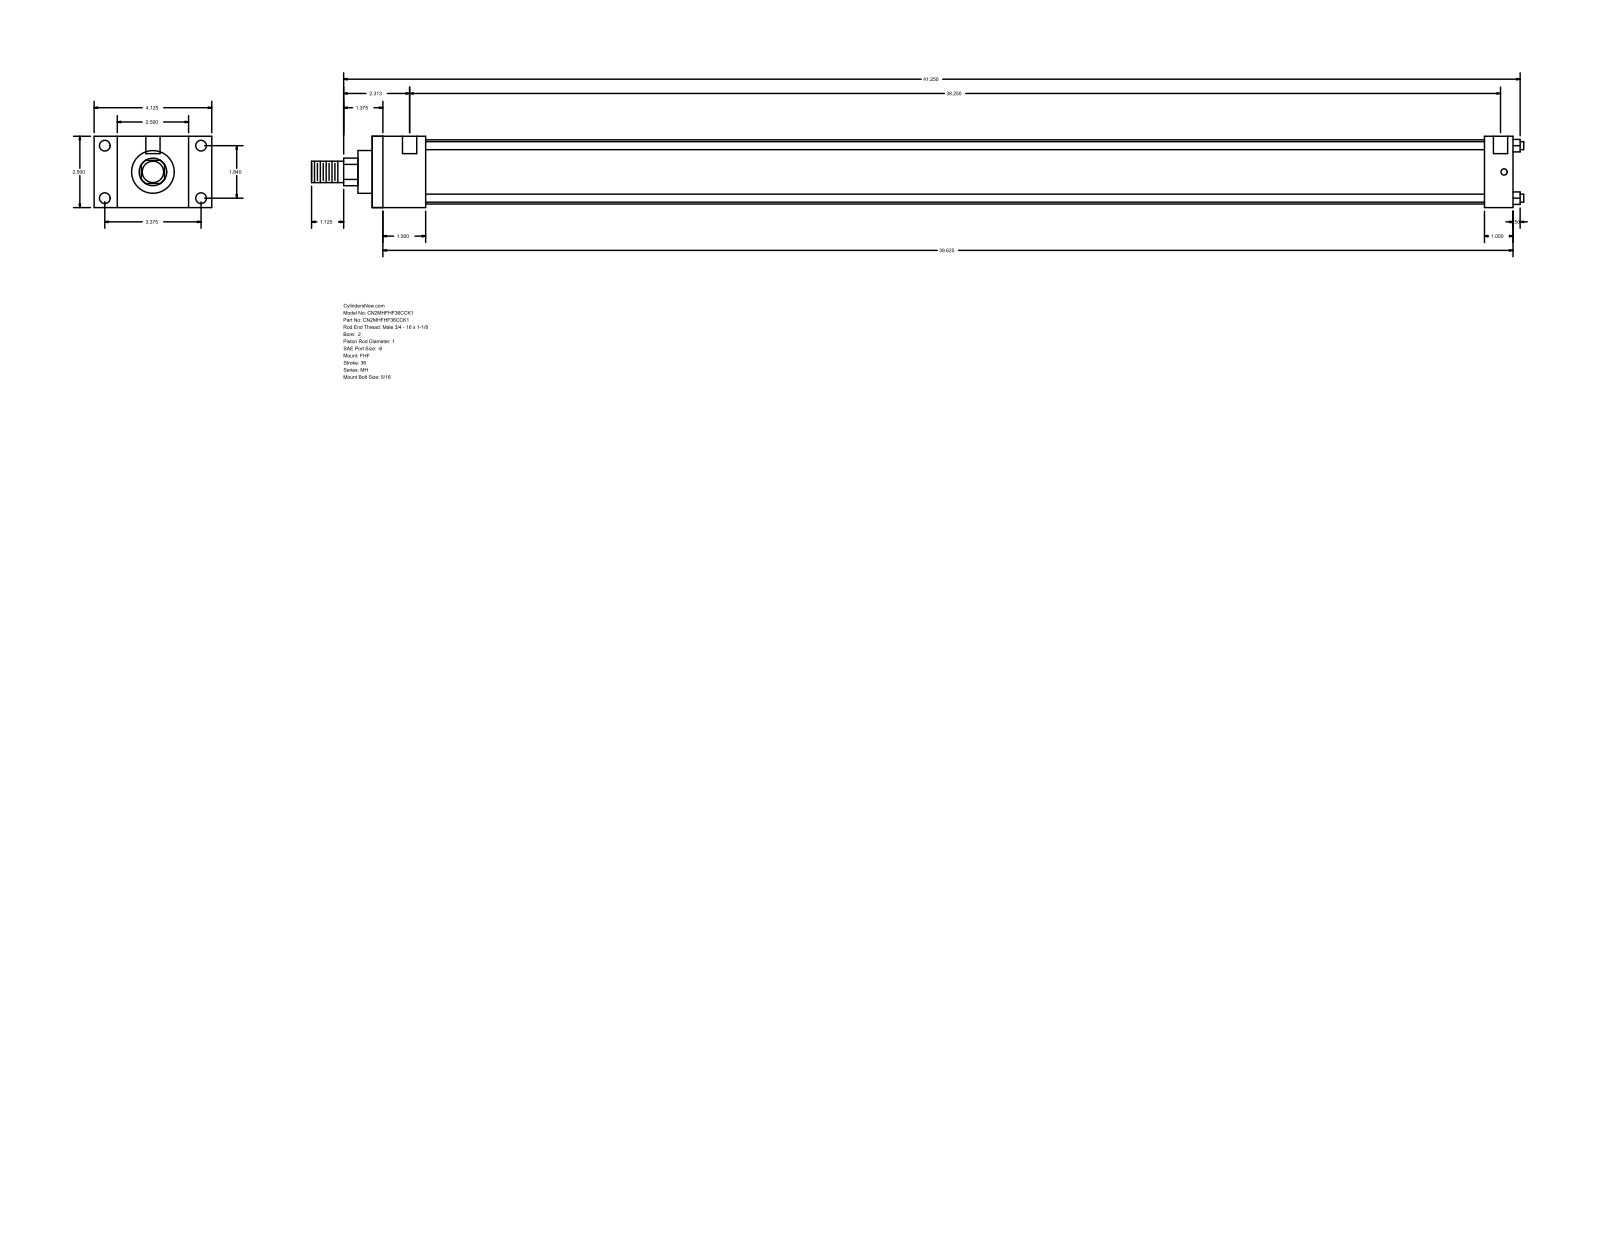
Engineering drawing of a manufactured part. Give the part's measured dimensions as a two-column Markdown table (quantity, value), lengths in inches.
| quantity | value |
| --- | --- |
| part name | MH_FHF__0200_1 |
| STEP written by | GSSL Pune (CONFIG_CONTROL_DESIGN) |
| units | inches |
| bodies | 0 solids, 88 faces (60 planar, 28 cylindrical, 0 other) |
| overall size | 42.5 × 4.125 × 2.5 |
| round holes (diameter × count) | 0.219 × 4, 0.375 × 4, 0.5 × 2 |
| round bosses / shafts (diameter × count) | 0.281 × 4, 2.25 × 1, 1.5 × 1, 1 × 1, 0.75 × 1 |
| partial cylindrical surfaces (radius × count) | 0.484 × 1 |
| main face-to-face distances | 2.5, 40, 1.875, 38.125, 0.813, 3.313, 4.125, 1, 39, 37.125 |
| hole center spacings | 1.84, 3.375, 3.844, 38.562, 0.125, 0.187, 38.25, 38.375 |
